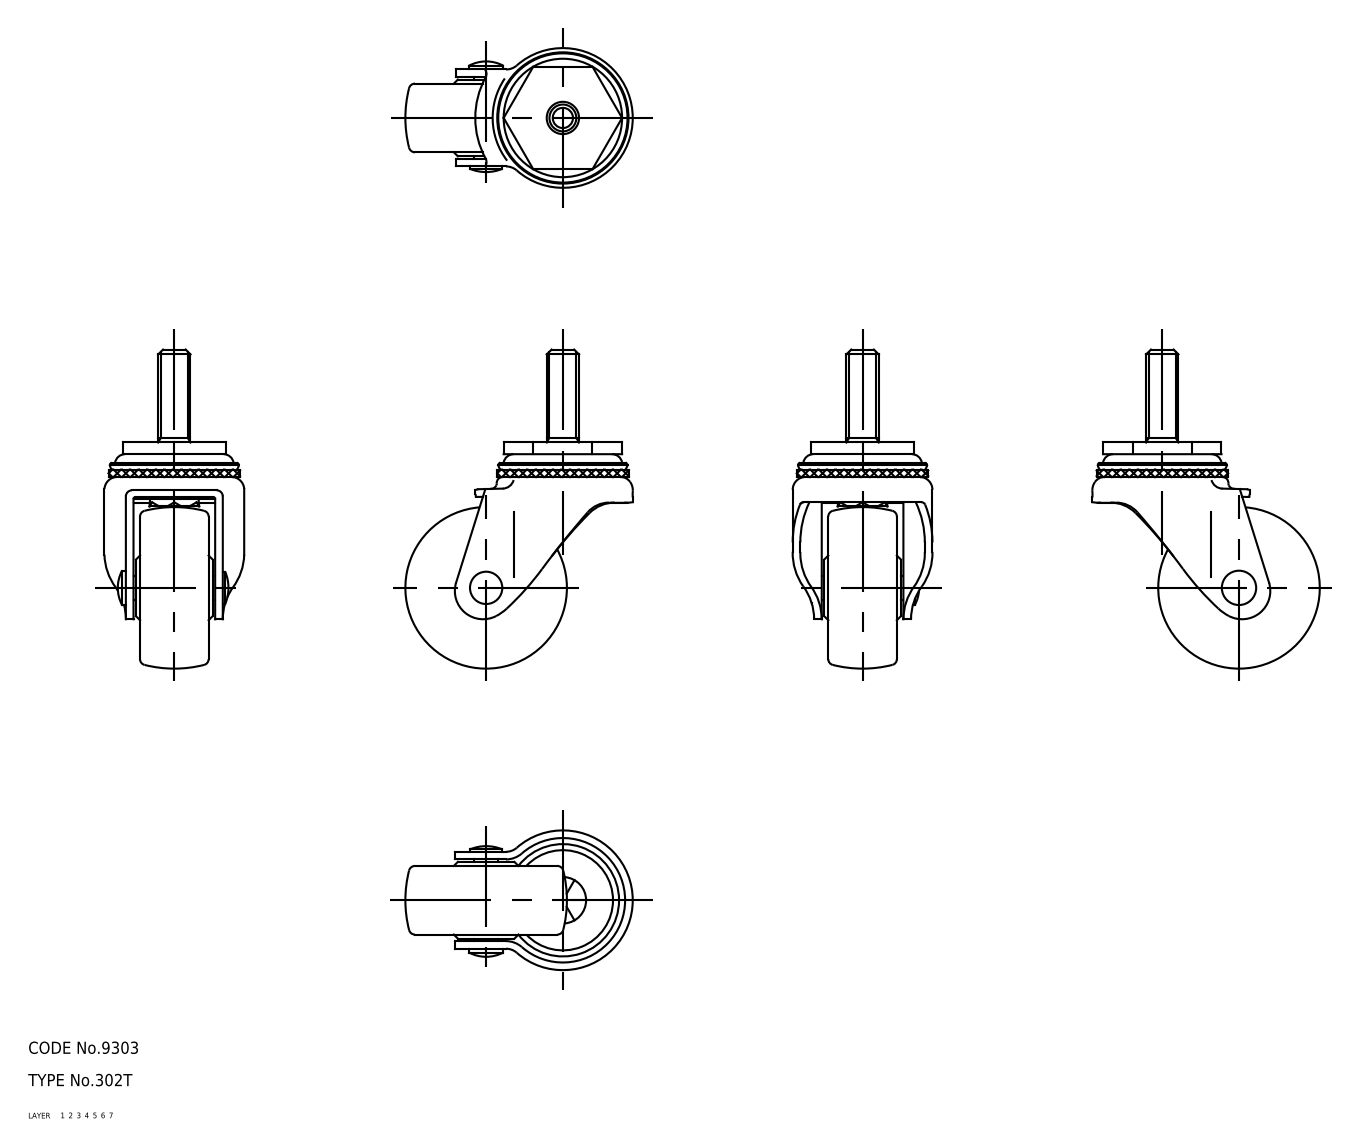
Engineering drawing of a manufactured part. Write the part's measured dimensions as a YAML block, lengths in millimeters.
part_name: "wheel; main shaft; axle; No_302T_23191_36"
step_written_by: "CADfix (AUTOMOTIVE_DESIGN)"
units: millimeters
bodies: {solids: 5, faces: 161, planar: 0, cylindrical: 0, other: 161}
overall_size: [79, 56.3, 34.6]
volume: 34292
surface_area: 14980
